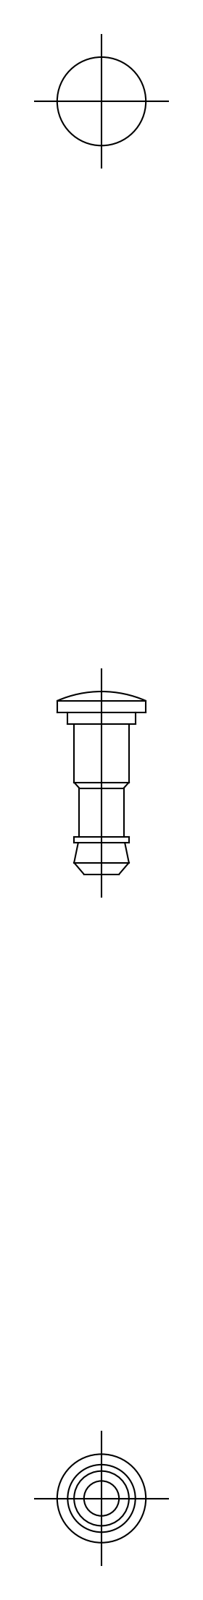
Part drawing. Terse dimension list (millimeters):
name: plunger
written by: CADfix (AUTOMOTIVE_DESIGN)
unit: mm
bodies: 1 solid, 22 faces (0 planar, 0 cylindrical, 22 other)
size: 15.7 × 7.6 × 7.6
volume: 278 mm³; area: 315 mm²
